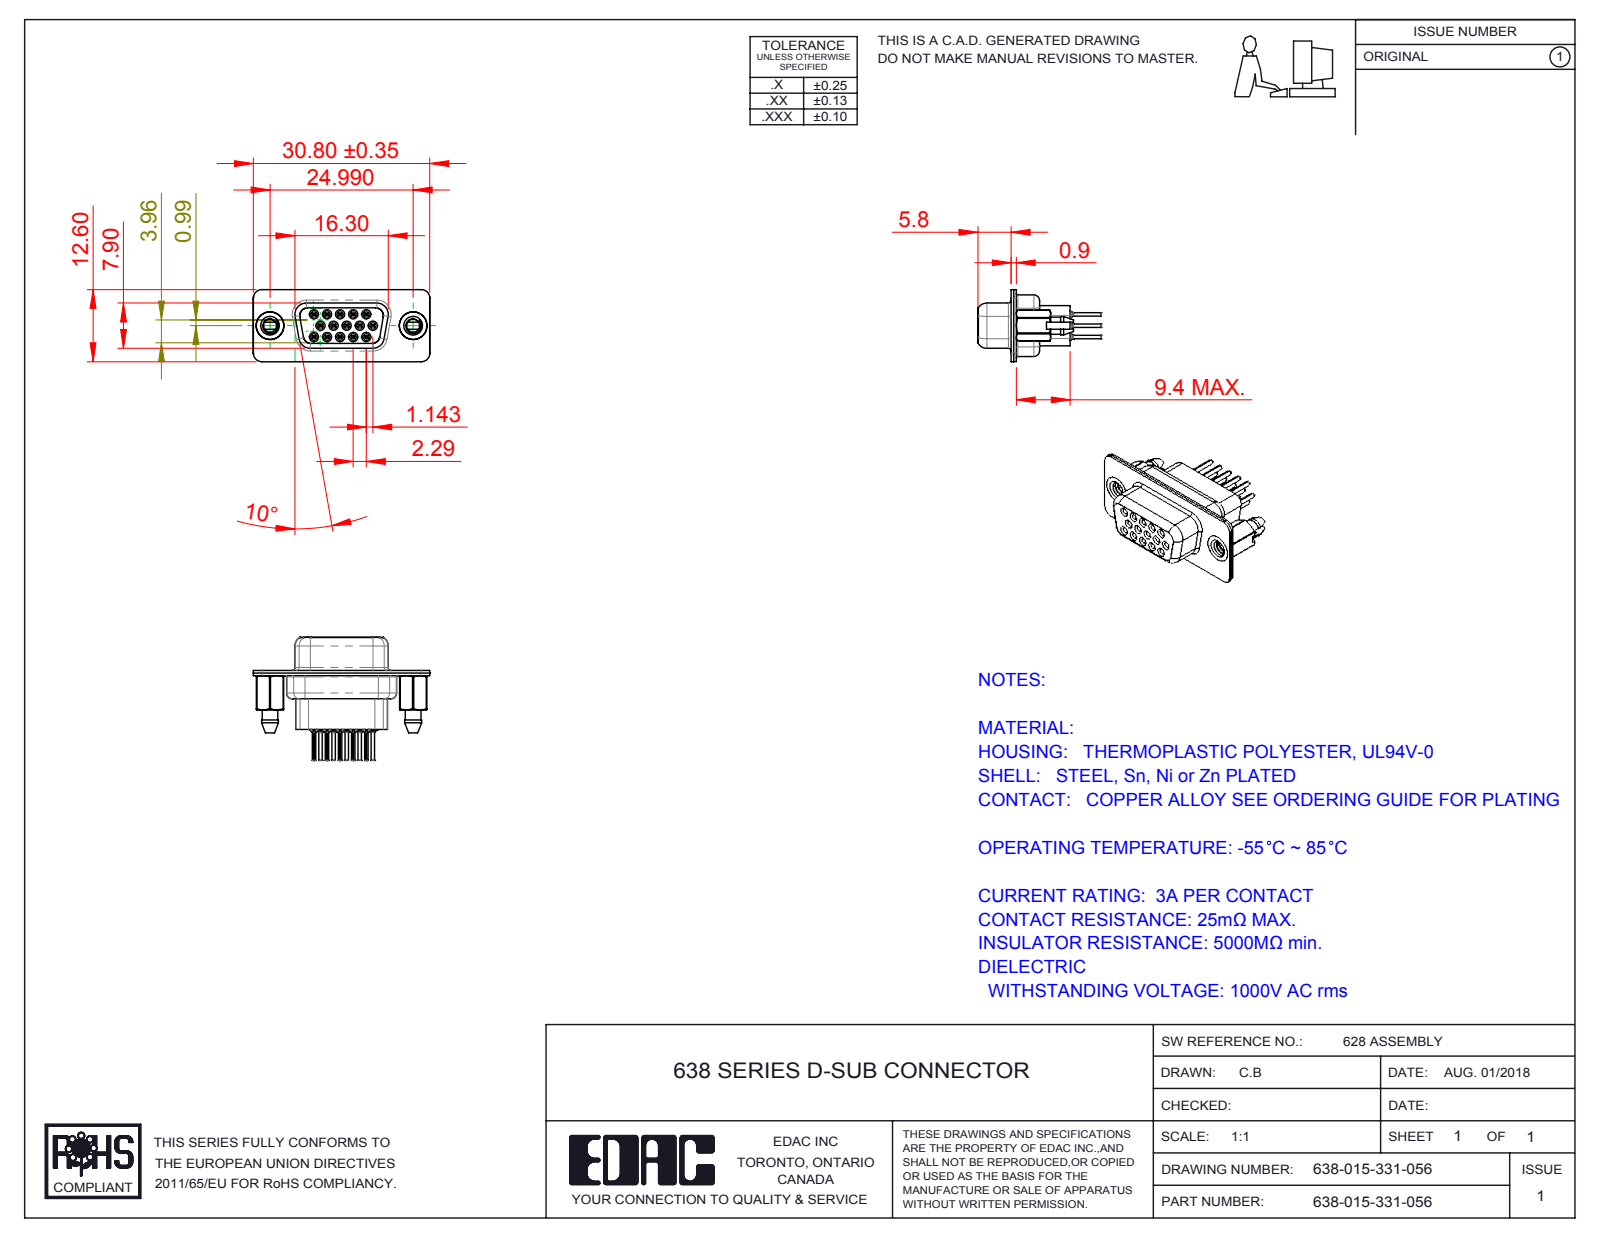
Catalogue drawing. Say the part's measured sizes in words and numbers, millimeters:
The part is named "638 Housing_15 Contacts HP; 638 Contact Row 1_31H; 638 Shell Rear_15 Contacts; 638 Shell Front_15 Contacts (+4 more)". Its 3-D file was written by "SolidWorks 2016 (CONFIG_CONTROL_DESIGN)". It is 20 solids with 2198 faces: 564 planar, 664 cylindrical and 970 other. Overall it measures 30.81 by 21.5 by 12.6 millimeters. Its volume is 1 996 cubic millimeters and its surface area 6 817 square millimeters. Round holes: 15 of diameter 0.2, 15 of diameter 0.8, 15 of diameter 1, 15 of diameter 1.1, 15 of diameter 1.6, 15 of diameter 1.7, 15 of diameter 1.8, 2 of diameter 2, 2 of diameter 2.26, 2 of diameter 4, 2 of diameter 4.05, 2 of diameter 4.85. Round bosses or shafts: 15 of diameter 2, 15 of diameter 1.5, 15 of diameter 1.2, 15 of diameter 0.6, 2 of diameter 4.95, 2 of diameter 4.8. Partial cylindrical surfaces (rounded edges, fillets, slot ends): 30 of radius 0.1, 22 of radius 1.5, 12 of radius 2, 10 of radius 0.28, 8 of radius 1.55, 5 of radius 1.35, 4 of radius 0.25, 4 of radius 0.5. The main face-to-face distances are 0.45, 0.9, 0.4, 1.43, 6.6, 8.88, 7, 2.28, 5.8, 9.4. The hole center spacings are 3.96, 2.28, 4.57, 2.29, 6.05, 6.04, 6.86, 7.92.
